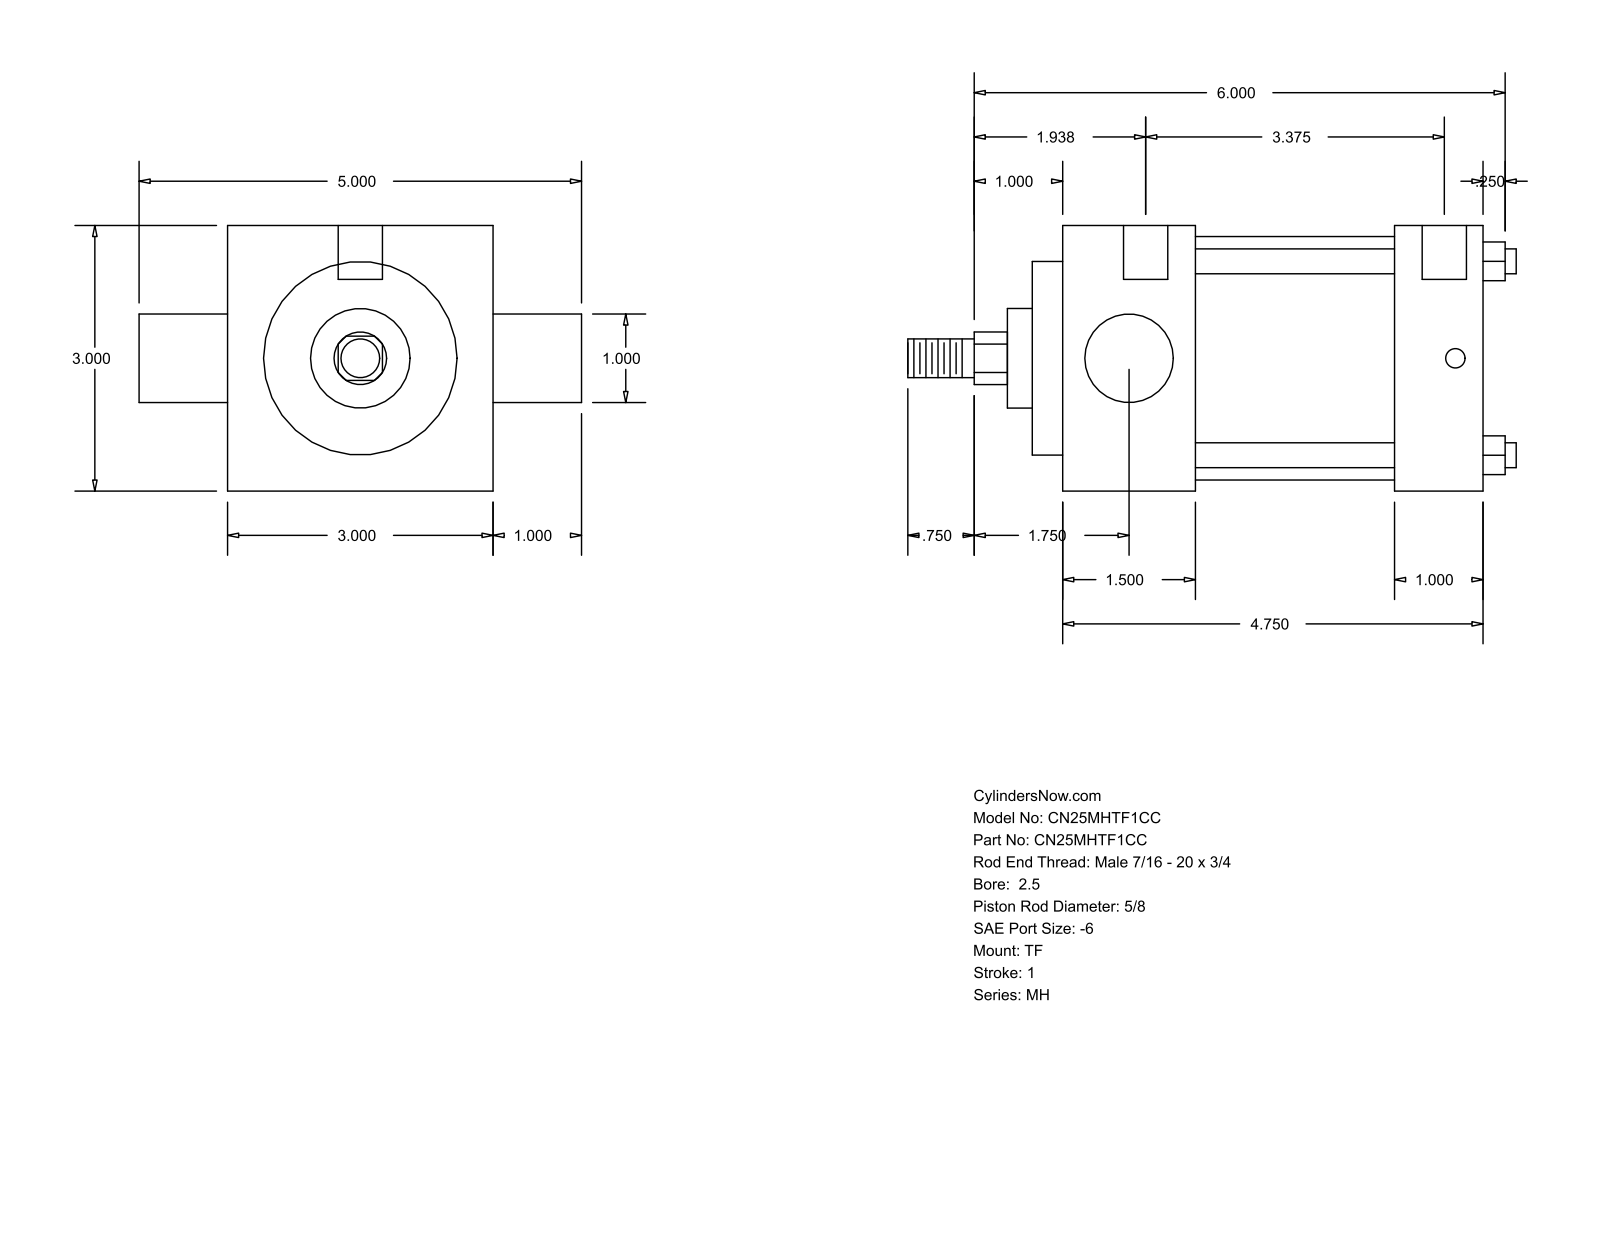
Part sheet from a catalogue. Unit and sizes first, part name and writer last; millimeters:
Units: millimetres
Overall size (bounding box): 174.62 × 127 × 76.2
Round holes (diameter × count): ⌀5.56 ×3, ⌀12.7 ×2
Round bosses / shafts (diameter × count): ⌀7.14 ×4, ⌀69.85 ×1, ⌀55.55 ×1, ⌀28.57 ×1, ⌀25.4 ×1, ⌀15.88 ×1, ⌀11.11 ×1
Partial cylindrical surfaces — rounded edges, fillets, slot ends (radius × count): R7.54 ×1
Main face-to-face distances: 76.2, 120.65, 25.4, 57.15, 82.55, 38.1, 95.25, 8.73, 46.83, 103.98
Hole centre spacings: 3.17, 4.76, 85.73, 88.9, 90.49, 93.66
Bodies: 0 solids, 86 faces (61 planar, 25 cylindrical, 0 other)
Part name (STEP PRODUCT): MH_TF__0250_0.625
STEP written by: GSSL Pune (CONFIG_CONTROL_DESIGN)
